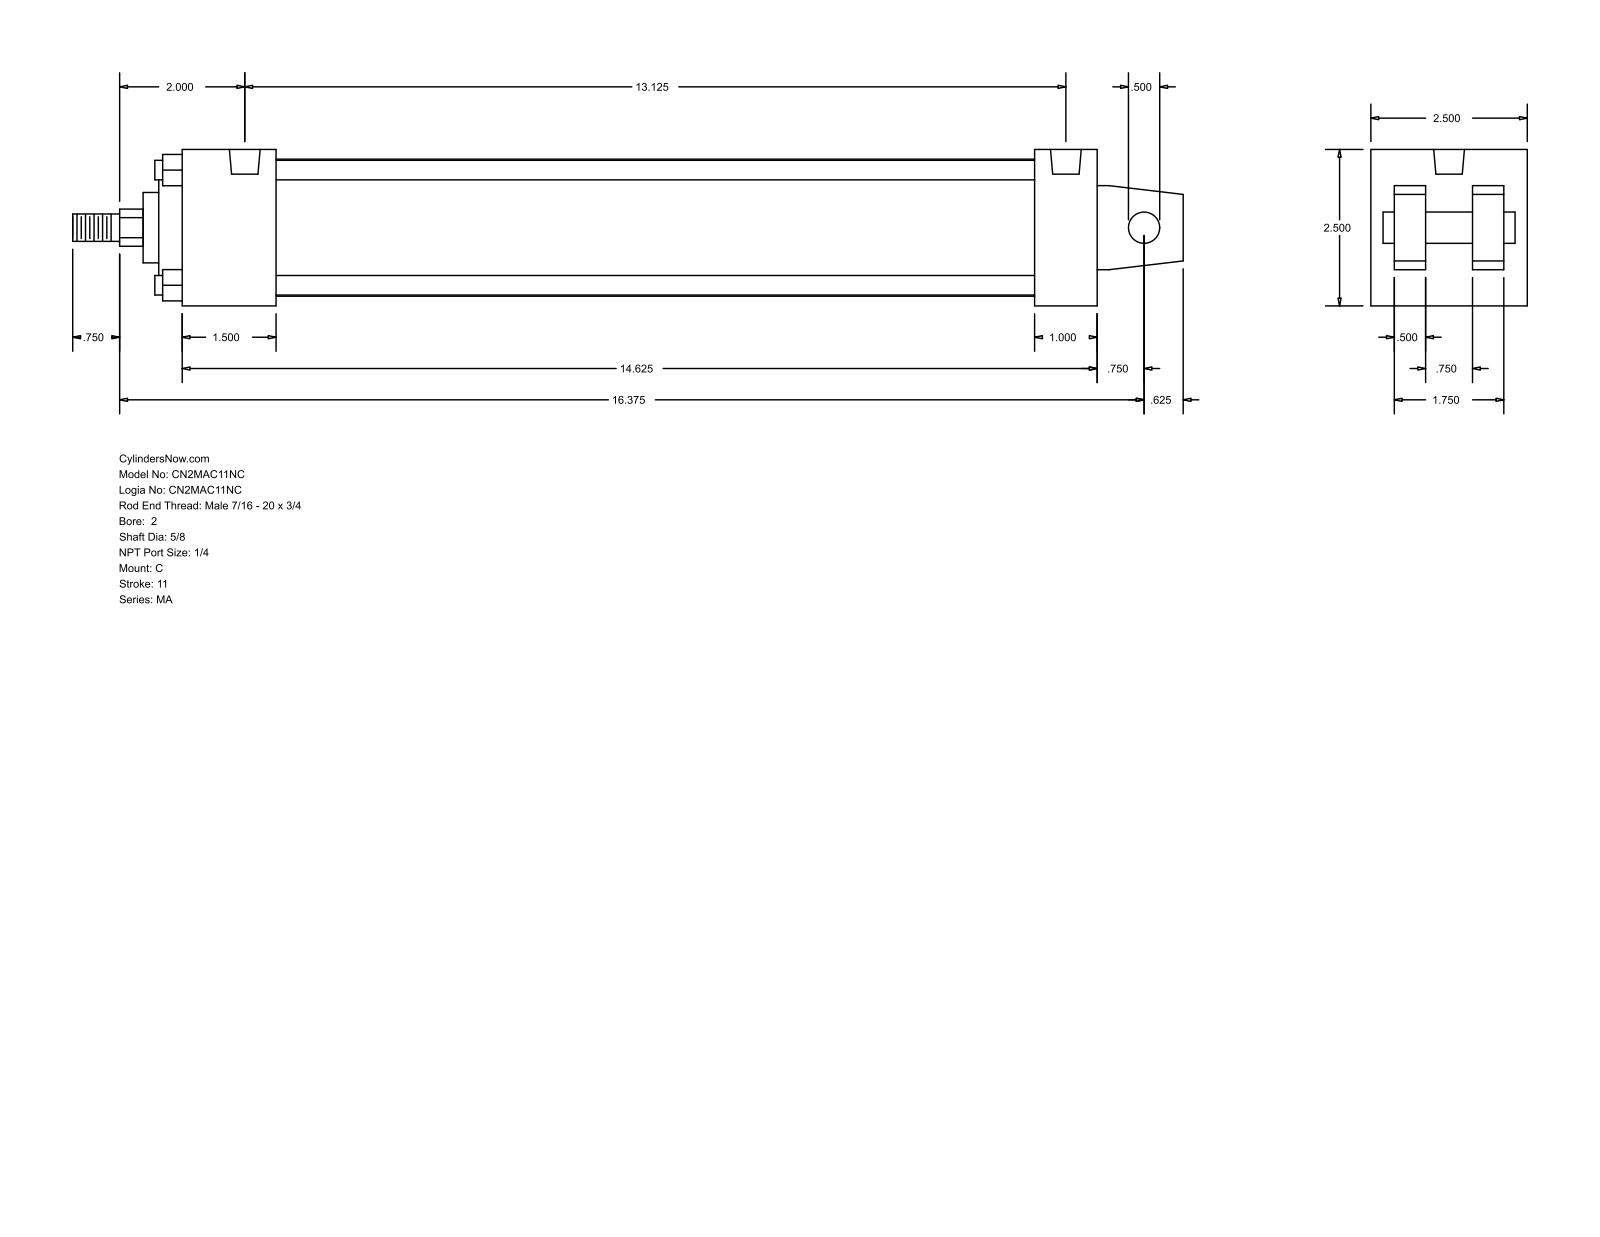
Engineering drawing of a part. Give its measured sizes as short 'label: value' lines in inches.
name: MA_C__0200_0.625
written by: GSSL Pune (CONFIG_CONTROL_DESIGN)
unit: in
bodies: 0 solids, 105 faces (77 planar, 28 cylindrical, 0 other)
size: 17.75 × 2.5 × 2.5
holes: 4× ⌀0.313, 2× ⌀0.492
bosses: 4× ⌀0.313, 1× ⌀2.19, 1× ⌀2, 1× ⌀1.125, 1× ⌀0.625, 1× ⌀0.5, 1× ⌀0.437
rounds: 1× R0.297
face distances: 2.5, 0.375, 0.5, 0.875, 1.625, 2.125, 1.25, 1, 1.5, 14.625
hole spacings: 13.125
